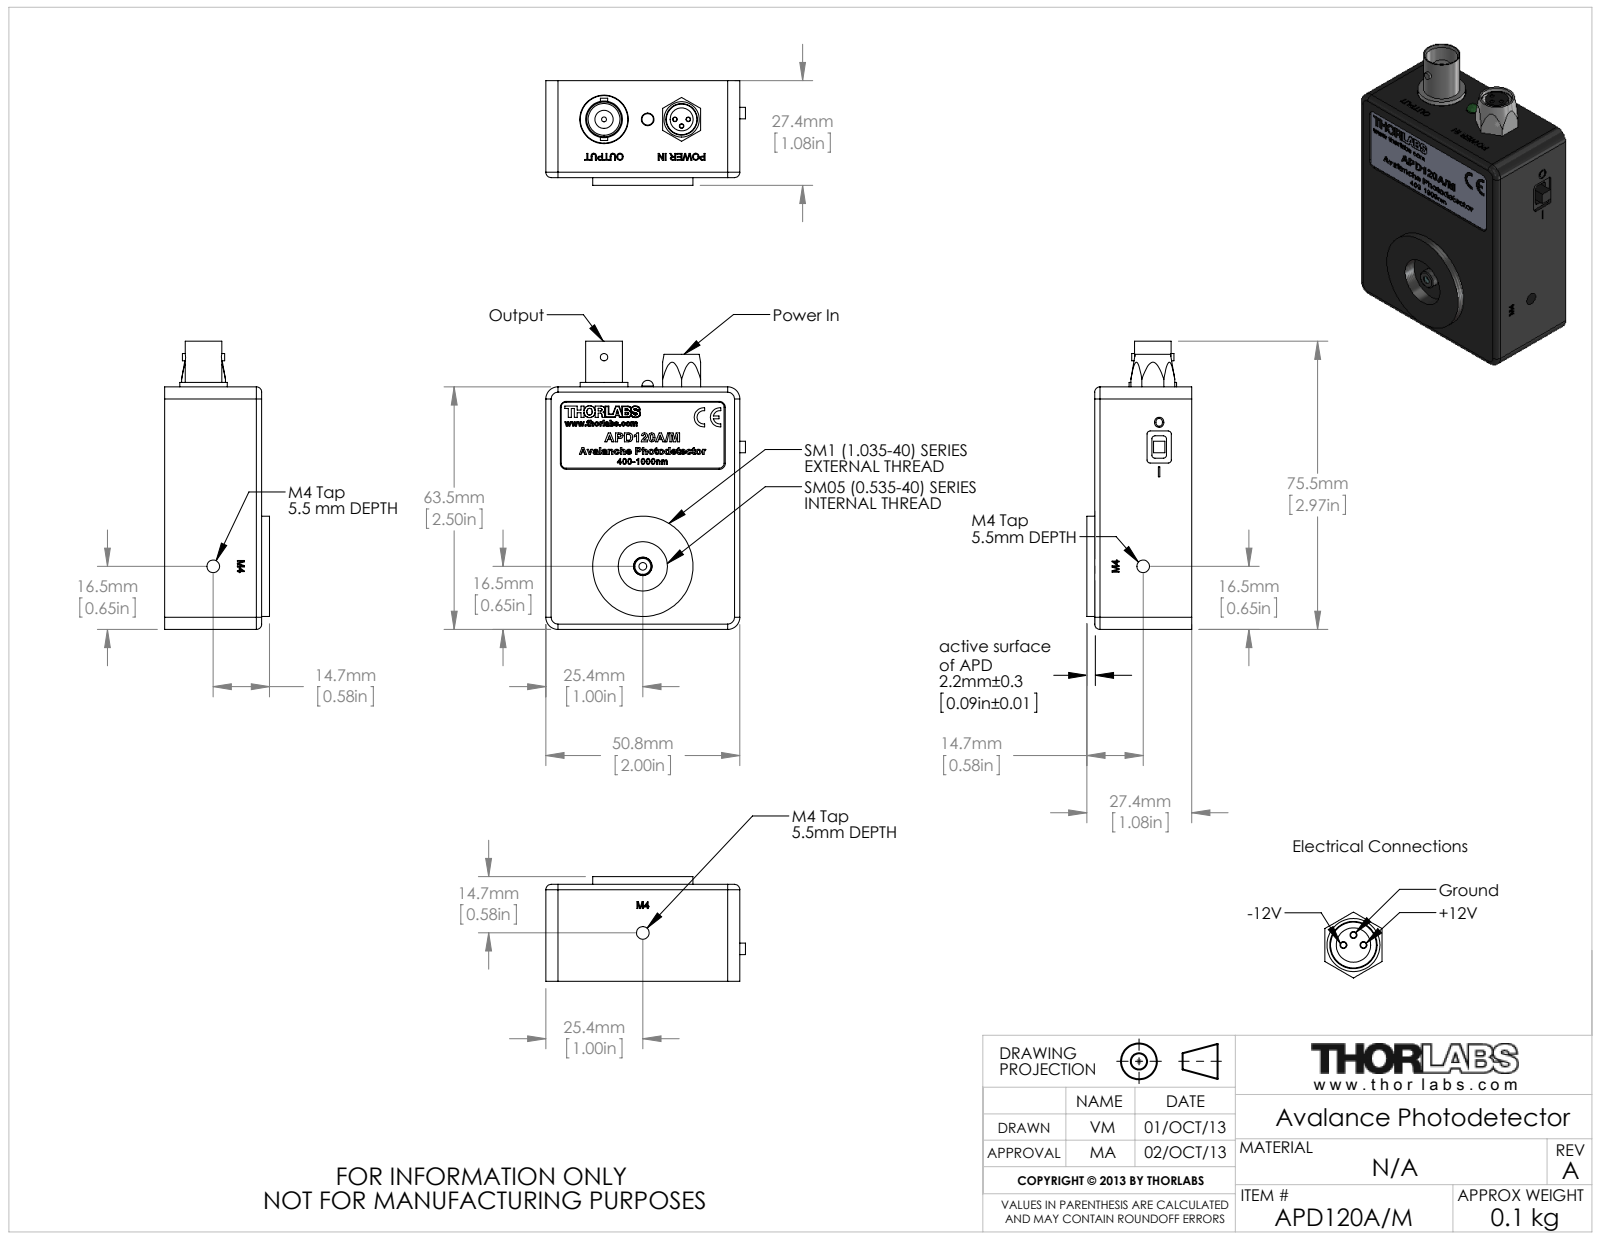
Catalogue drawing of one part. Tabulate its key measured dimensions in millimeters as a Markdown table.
| quantity | value |
| --- | --- |
| part name | APD120AM; APD120x-Folie_APD120A-M; countersunk flat head cross recess screw_din_ISO 7046-1 - M2 x 4 - Z --- 4N; M0092-0545-0A-Deckel (+7 more) |
| STEP written by | SolidWorks 2012 (CONFIG_CONTROL_DESIGN) |
| units | millimeters |
| bodies | 76 solids, 2271 faces (1455 planar, 283 cylindrical, 533 other) |
| overall size | 75.46 × 52.26 × 27.43 |
| volume | 39 549 mm³ |
| surface area | 33 779 mm² |
| round holes (diameter × count) | 1.6 × 8, 2.4 × 4, 2.44 × 4, 0.46 × 3, 1 × 3, 1.02 × 3, 3.3 × 2, 1.27 × 1, 1.32 × 1, 2 × 1, 2.5 × 1, 3.3 × 1 |
| round bosses / shafts (diameter × count) | 0.51 × 6, 3.8 × 5, 2 × 4, 0.45 × 3, 26.29 × 1, 12.45 × 1, 10.92 × 1, 9.6 × 1 |
| partial cylindrical surfaces (radius × count) | 3.17 × 18, 3.3 × 14, 0.8 × 10, 0.79 × 8, 1.91 × 8, 2.41 × 8, 1.27 × 4, 1.4 × 4 |
| main face-to-face distances | 1.59, 11.49, 13.08, 2.54, 9.89, 1.6, 11.48, 25.4, 23.81, 13.92 |
| hole center spacings | 41.17, 39.38, 4.41, 20.89, 21.35, 51.14, 65.51, 1.27 |
